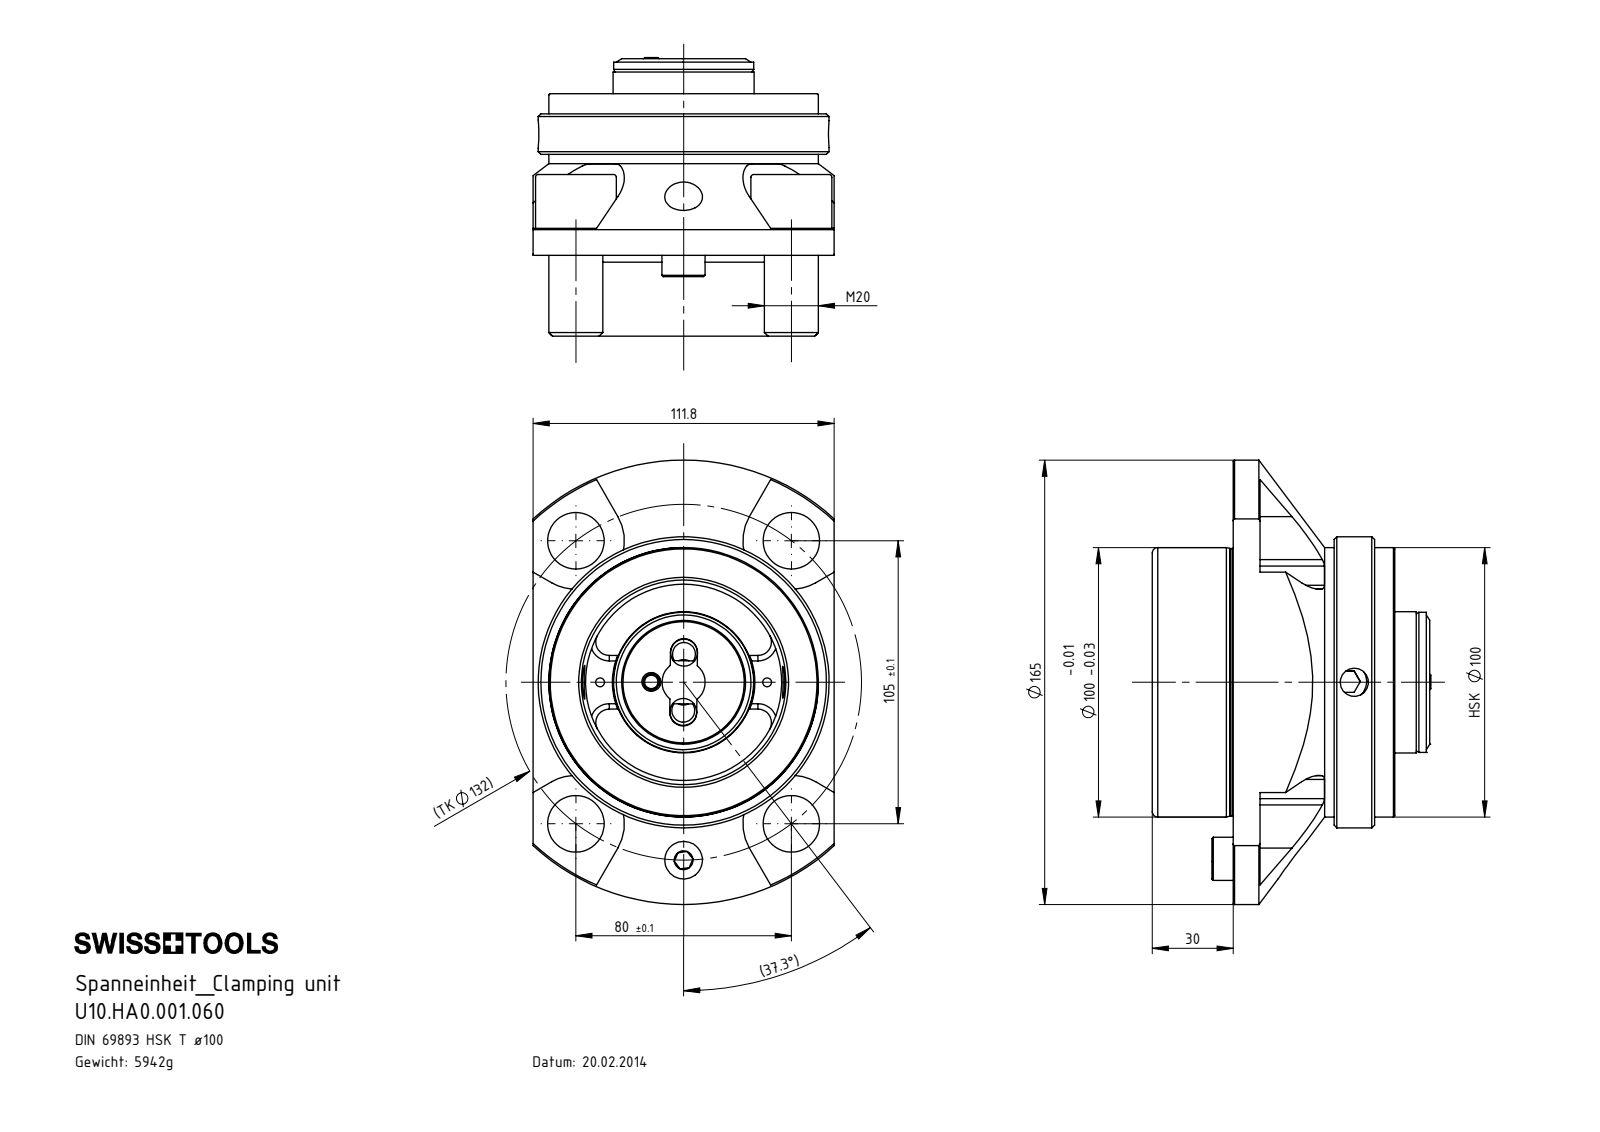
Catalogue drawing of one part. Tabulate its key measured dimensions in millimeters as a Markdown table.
| quantity | value |
| --- | --- |
| part name | U10-HA0.001.060_C; Grundkörper0; O-Ring; Dichtung0 (+8 more) |
| STEP written by | SolidWorks 2012 (CONFIG_CONTROL_DESIGN) |
| units | millimeters |
| bodies | 16 solids, 503 faces (187 planar, 176 cylindrical, 140 other) |
| overall size | 164.9 × 111.8 × 103.4 |
| volume | 849 278 mm³ |
| surface area | 164 793 mm² |
| round holes (diameter × count) | 14 × 4, 21 × 4, 3.3 × 2, 8.5 × 2, 10 × 2, 4.5 × 1, 6 × 1, 7 × 1, 10.25 × 1, 10.5 × 1, 11 × 1, 12 × 1 |
| round bosses / shafts (diameter × count) | 30 × 4, 20 × 4, 16 × 2, 108 × 1, 100 × 1, 99.3 × 1, 52.4 × 1, 52 × 1 |
| partial cylindrical surfaces (radius × count) | 5 × 14, 4 × 6, 4.85 × 4, 8 × 4, 18 × 4, 3 × 3, 1 × 1, 5.05 × 1 |
| main face-to-face distances | 30, 40, 10, 60, 50, 90, 111.8, 19.5, 38.9, 8.9 |
| hole center spacings | 66, 53.27, 88.3, 11, 16.28, 31, 32.76, 33.03 |
